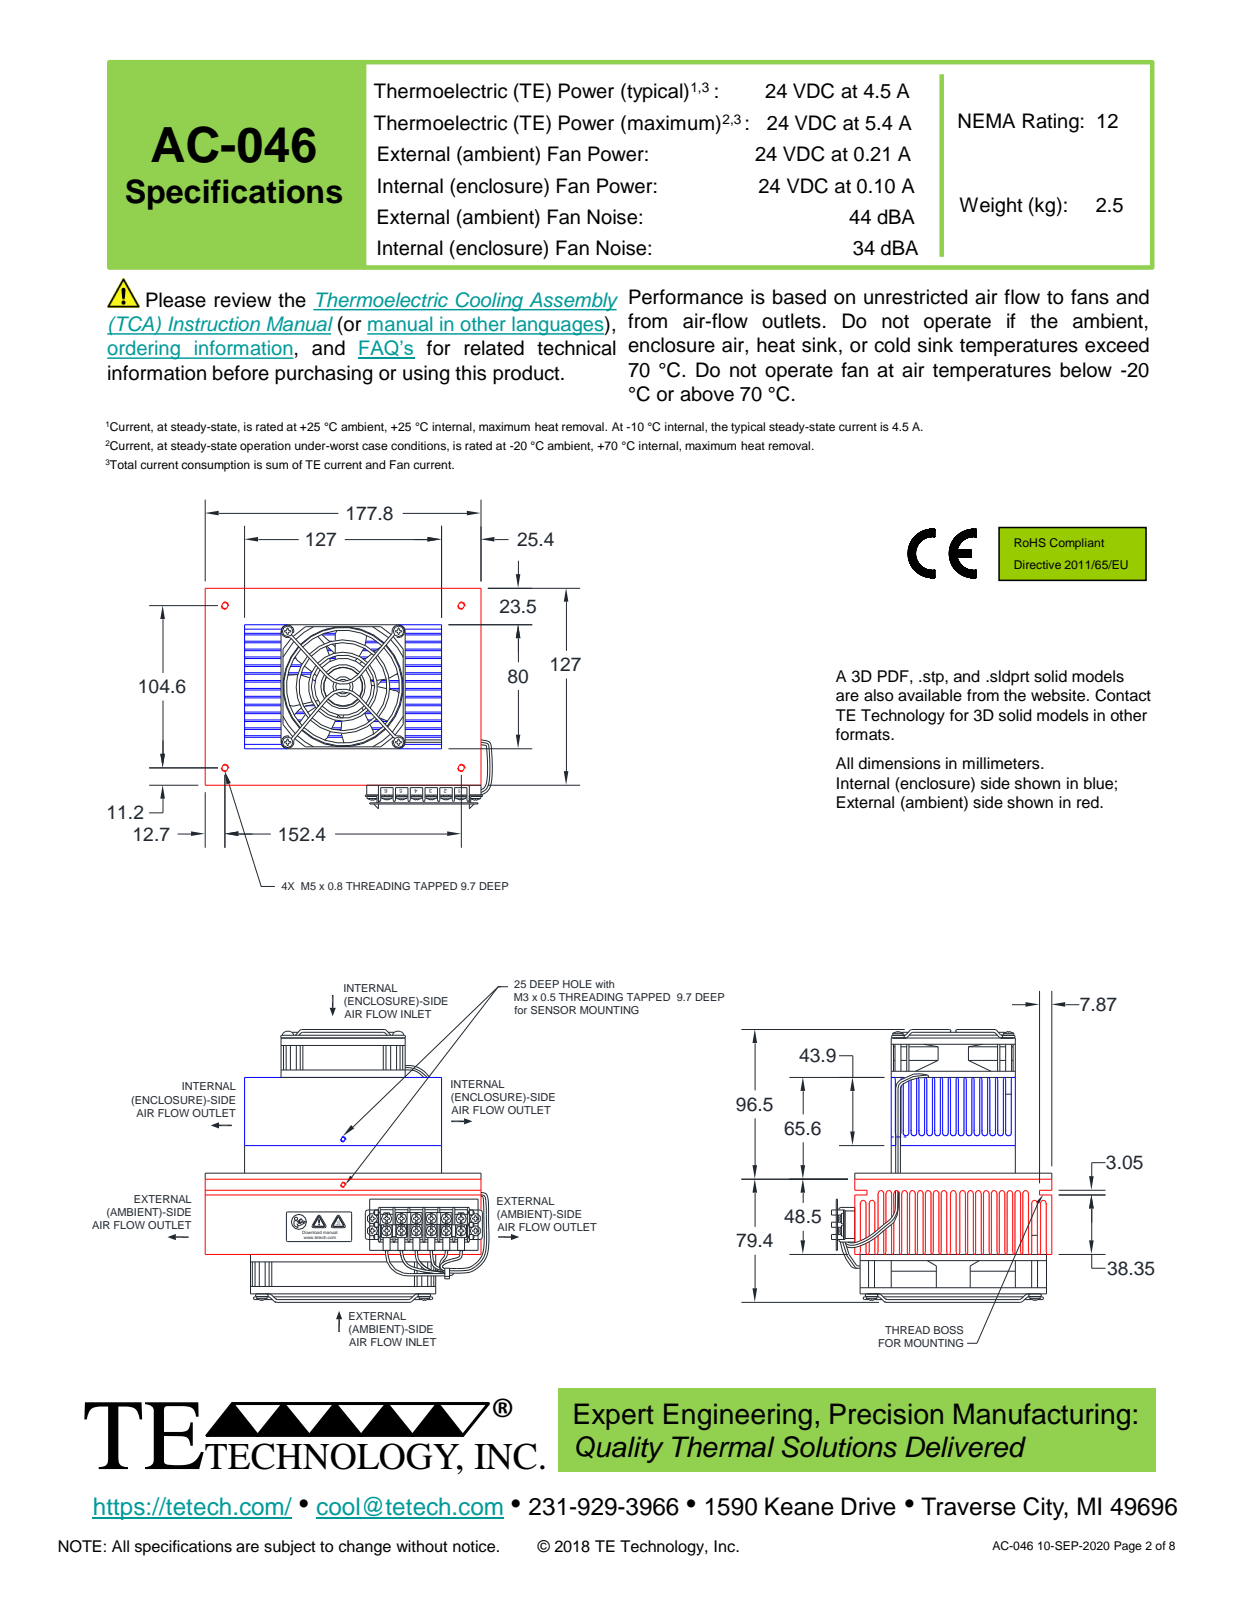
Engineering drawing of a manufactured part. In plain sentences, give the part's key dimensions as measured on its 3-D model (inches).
The part is named "2660 AC-046 inner gasket; 3175 AC-046 outer-gasket; 4775 AC-046 cold sink; cover-clip (+8 more)". Its 3-D file was written by "Alibre (AUTOMOTIVE_DESIGN)". It is 142 solids with 3974 faces: 2218 planar, 811 cylindrical and 945 other. Overall it measures 7.03 by 6.953 by 5.598 inches. Its volume is 74.2 cubic inches and its surface area 1 244 square inches. Round holes: 19 of diameter 0.104, 8 of diameter 0.169, 7 of diameter 0.25, 6 of diameter 0.075, 6 of diameter 0.139, 6 of diameter 0.155, 4 of diameter 0.163, 4 of diameter 0.17, 4 of diameter 0.185, 3 of diameter 0.12, 3 of diameter 0.164, 3 of diameter 0.166. Round bosses or shafts: 24 of diameter 0.057, 19 of diameter 0.138, 19 of diameter 0.071, 16 of diameter 0.27, 12 of diameter 0.062, 8 of diameter 0.322, 8 of diameter 0.164, 6 of diameter 0.193. Partial cylindrical surfaces (rounded edges, fillets, slot ends): 59 of radius 0.039, 54 of radius 0.03, 52 of radius 0.01, 34 of radius 0.028, 24 of radius 0.02, 24 of radius 0.031, 21 of radius 0.037, 15 of radius 0.079. The main face-to-face distances are 0.2, 0.4, 0.6, 0.8, 1, 2.075, 1.875, 2.275, 1.675, 2.475. The hole center spacings are 0.75, 0.375, 0.31, 0.811, 0.375, 0.486, 1.125, 1.5.
